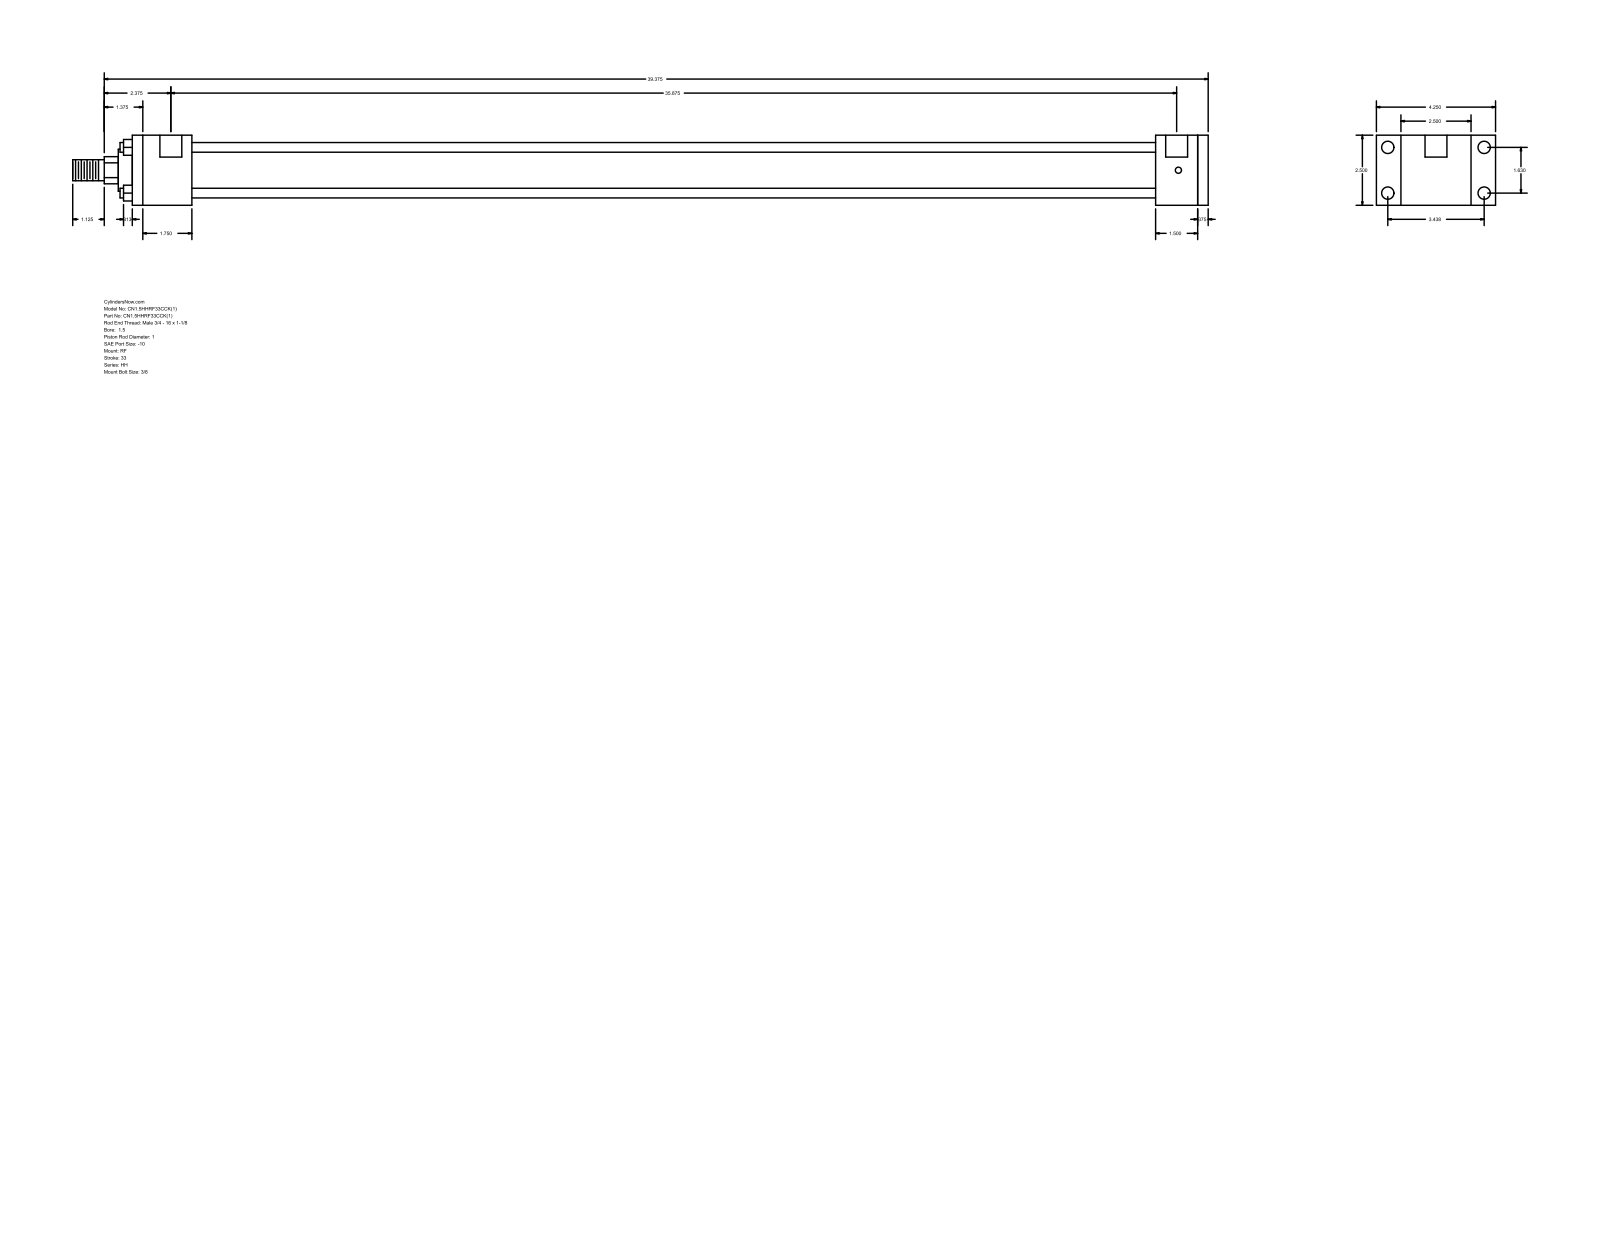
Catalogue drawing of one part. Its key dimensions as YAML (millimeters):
part_name: "HH_RF__0150_1"
step_written_by: "GSSL Pune (CONFIG_CONTROL_DESIGN)"
units: millimeters
bodies: {solids: 0, faces: 92, planar: 64, cylindrical: 28, other: 0}
overall_size: [1028.7, 107.95, 63.5]
round_holes:
  - {diameter: 5.56, count: 4}
  - {diameter: 11.13, count: 4}
  - {diameter: 19.84, count: 2}
round_bosses_or_shafts:
  - {diameter: 8.76, count: 4}
  - {diameter: 44.45, count: 1}
  - {diameter: 38.1, count: 1}
  - {diameter: 25.4, count: 1}
  - {diameter: 19.05, count: 1}
partial_cylinders:
  - {radius: 12.29, count: 1}
face_to_face_distances: [63.5, 9.52, 38.1, 873.12, 911.22, 920.74, 47.62, 53.98, 927.1, 965.2]
hole_center_spacings: [1.59, 41.4, 87.32, 96.64, 912.81, 914.4, 911.22]
